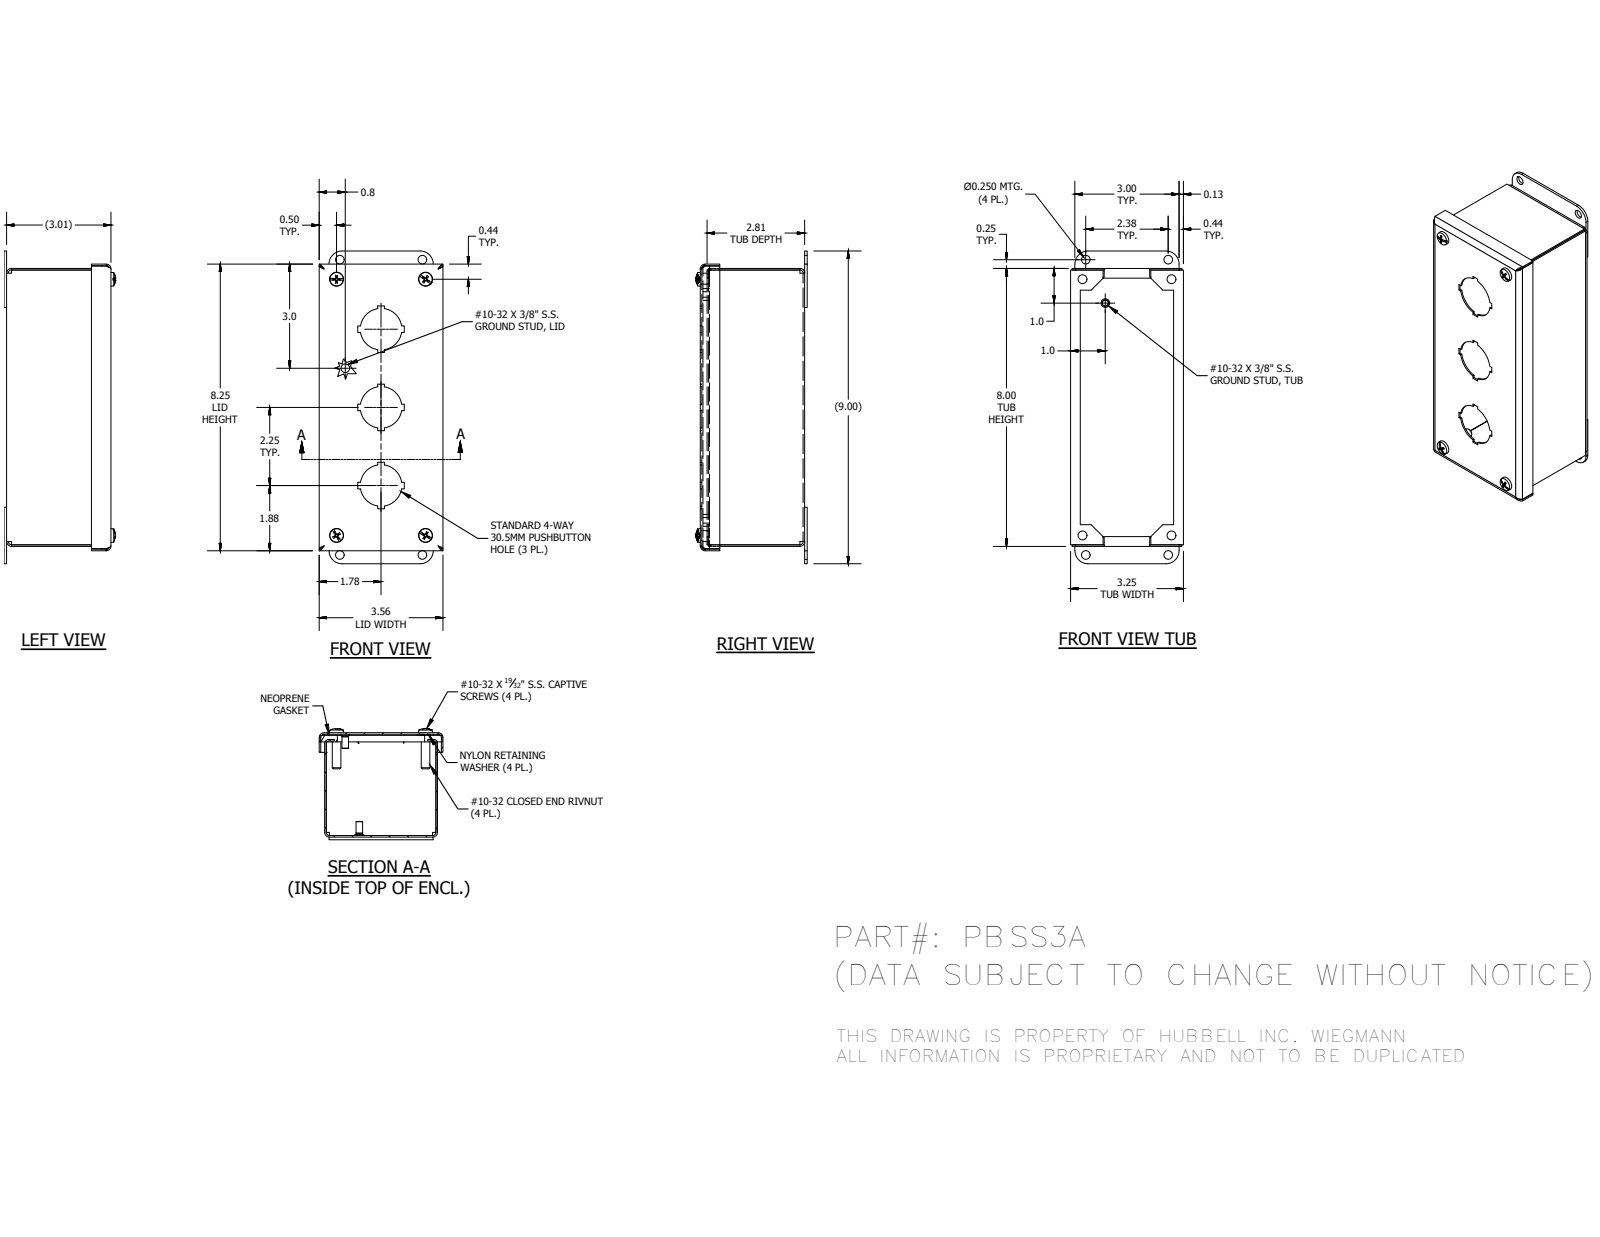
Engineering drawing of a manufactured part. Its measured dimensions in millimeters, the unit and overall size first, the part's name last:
Units: millimetres
Overall size (bounding box): 228.6 × 90.49 × 81.29
Round holes (diameter × count): ⌀3.96 ×4, ⌀4.98 ×4, ⌀6.35 ×4, ⌀6.53 ×4, ⌀7.06 ×4, ⌀7.14 ×4, ⌀7.95 ×4, ⌀30.48 ×3, ⌀3.38 ×2
Round bosses / shafts (diameter × count): ⌀11.51 ×4, ⌀10.31 ×4, ⌀6.3 ×4, ⌀4.25 ×4, ⌀6.35 ×2, ⌀4.83 ×2
Partial cylindrical surfaces — rounded edges, fillets, slot ends (radius × count): R2.38 ×8, R3.52 ×8, R2.27 ×4, R9.53 ×4, R1.59 ×3, R2.73 ×2, R2.73 ×2, R1.59 ×1
Main face-to-face distances: 1.14, 1.15, 74.04, 75.19, 75.18, 76.33, 81.4, 82.55, 80.26, 81.41
Hole centre spacings: 0.48, 48.91, 99.15, 154.28, 187.77, 201.62, 14.07, 14.48
Volume: 145 370 mm³ · Surface area: 207 558 mm²
Bodies: 20 solids, 584 faces (368 planar, 108 cylindrical, 108 other)
Part name (STEP PRODUCT): PBSS3ALID; 37210; 39077; PBSS3ABKP (+5 more)
STEP written by: Autodesk Inventor 2016 (AUTOMOTIVE_DESIGN)
